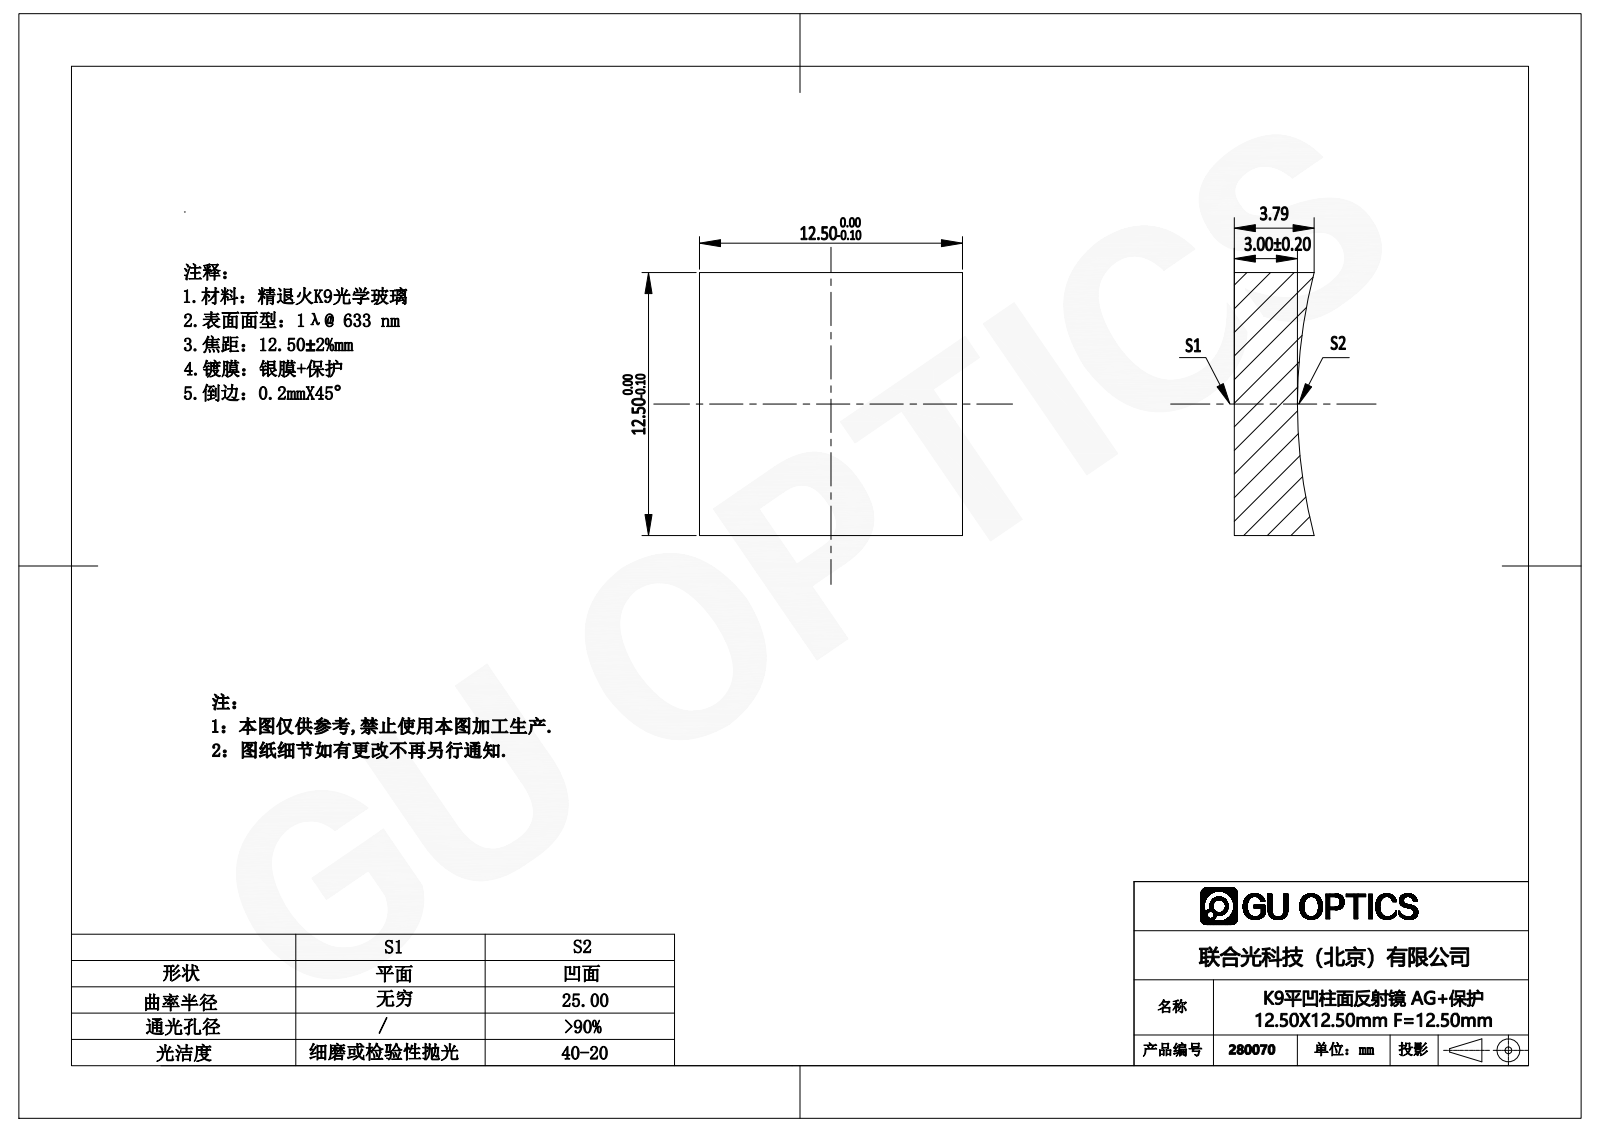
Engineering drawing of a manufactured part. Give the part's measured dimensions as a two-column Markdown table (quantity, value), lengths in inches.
| quantity | value |
| --- | --- |
| part name | 280004 |
| STEP written by | SolidWorks 2016 (AUTOMOTIVE_DESIGN) |
| units | inches |
| bodies | 1 solid, 7 faces (5 planar, 2 cylindrical, 0 other) |
| overall size | 0.492 × 0.492 × 0.149 |
| volume | 0.031 in³ |
| surface area | 0.761 in² |
| partial cylindrical surfaces (radius × count) | 0.984 × 1 |
| main face-to-face distances | 0.492 |
